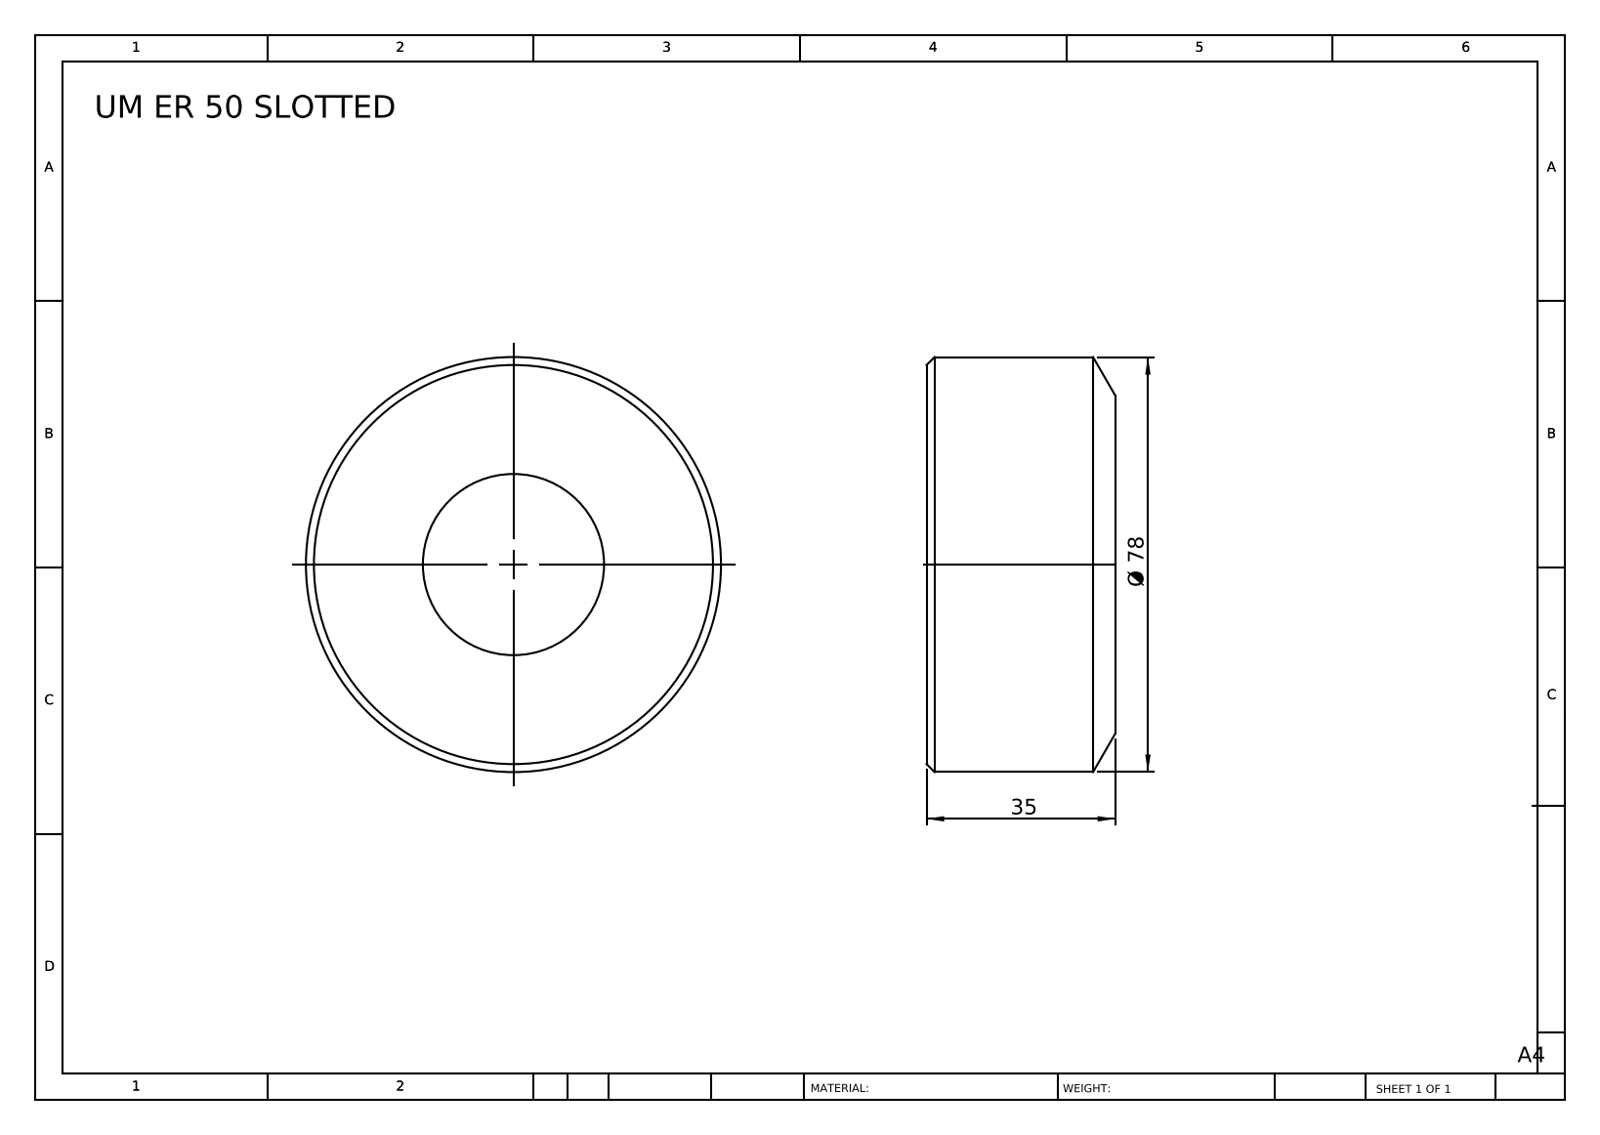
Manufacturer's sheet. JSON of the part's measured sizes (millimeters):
{"part_name": "UM ER 50 SLOTTED", "step_written_by": "SolidWorks 2014 (CONFIG_CONTROL_DESIGN)", "units": "millimeters", "bodies": {"solids": 1, "faces": 10, "planar": 2, "cylindrical": 4, "other": 4}, "overall_size": [77.9, 77.9, 35.4], "volume_mm3": 132872, "surface_area_mm2": 19173, "round_holes": [[34, 1]], "round_bosses_or_shafts": [[77.9, 1]], "face_to_face_distances": [35.4]}
